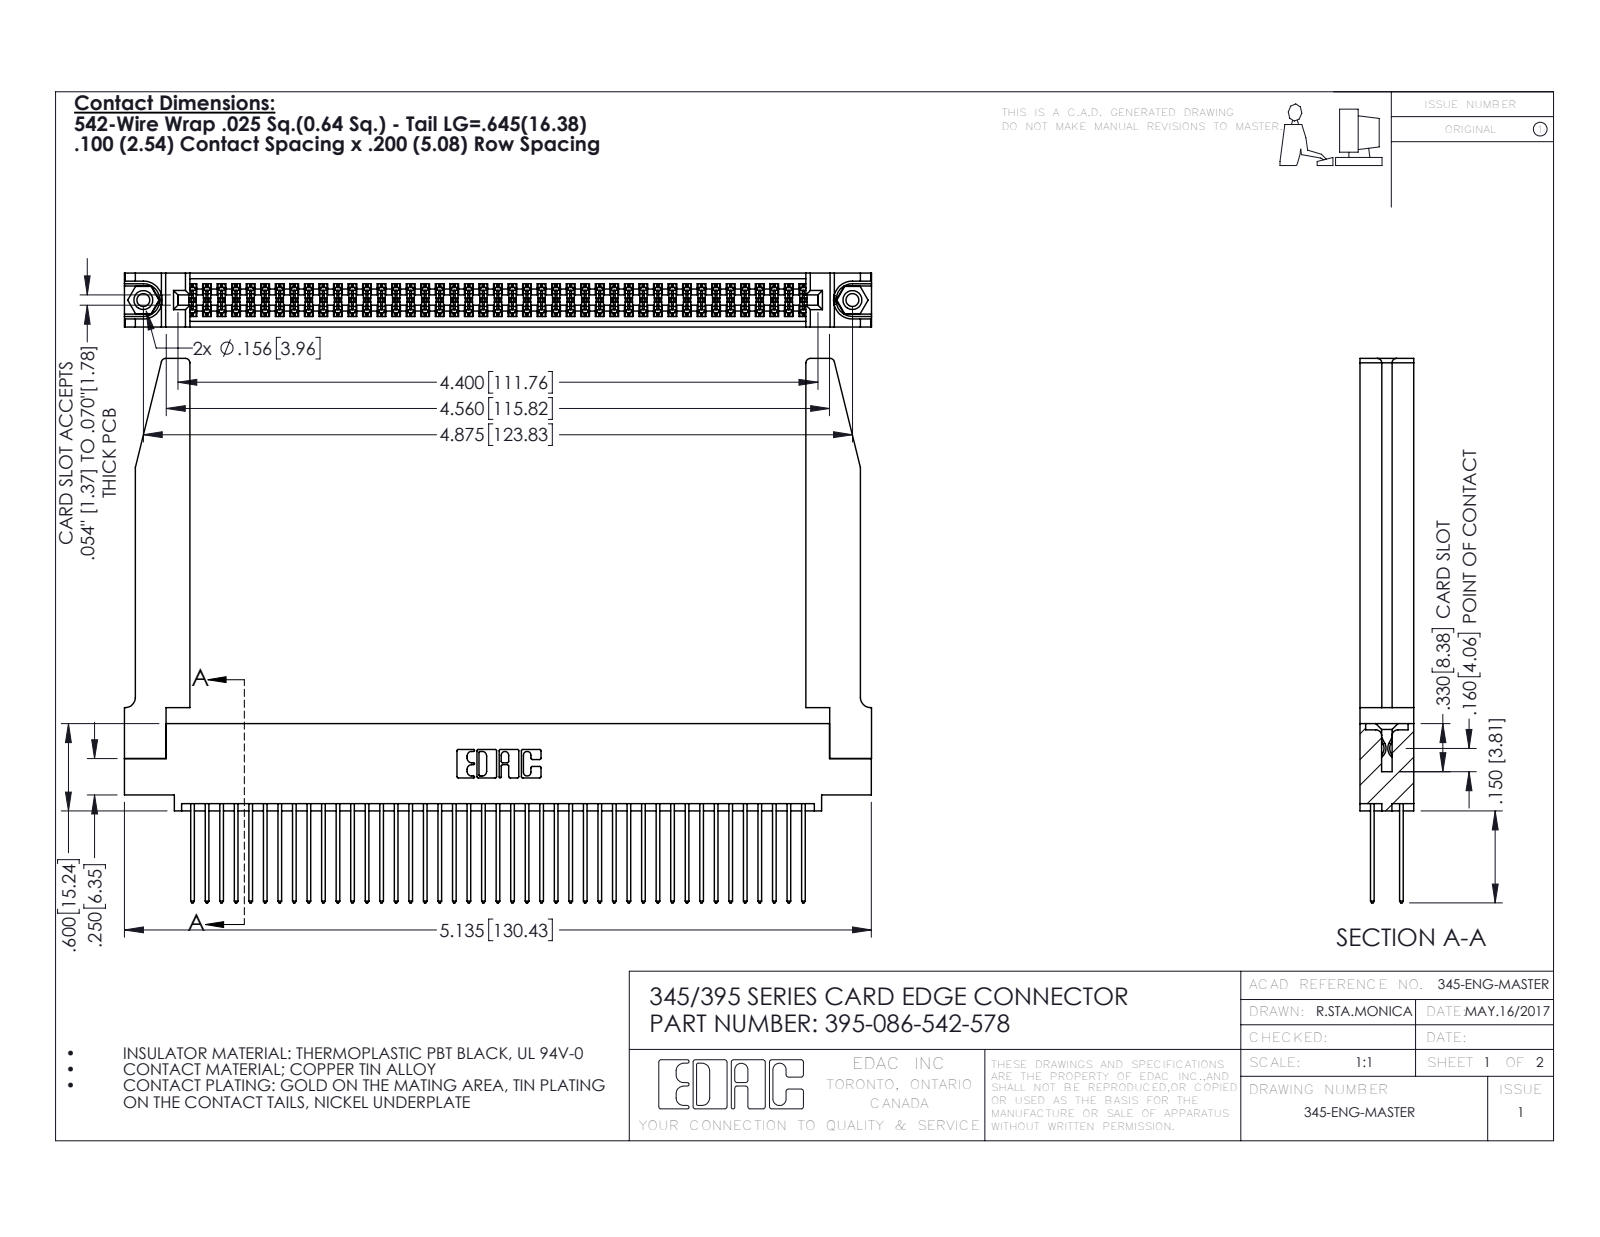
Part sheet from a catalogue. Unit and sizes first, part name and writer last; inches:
Units: inches
Overall size (bounding box): 5.136 × 3.742 × 0.37
Round holes (diameter × count): ⌀0.089 ×2, ⌀0.125 ×2, ⌀0.156 ×2, ⌀0.064 ×1
Round bosses / shafts (diameter × count): ⌀0.155 ×2
Partial cylindrical surfaces — rounded edges, fillets, slot ends (radius × count): R0.006 ×129, R0.01 ×86, R0.01 ×22, R0.03 ×8, R0.007 ×6, R0.031 ×6, R0.026 ×3, R0.014 ×2
Main face-to-face distances: 0.072, 0.298, 0.37, 0.2, 0.098, 0.272, 0.025, 0.225, 0.175, 0.148
Hole centre spacings: 0.27, 4.639, 4.875
Volume: 1.268 in³ · Surface area: 43.48 in²
Bodies: 91 solids, 4664 faces (3064 planar, 1548 cylindrical, 52 other)
Part name (STEP PRODUCT): 345-250-001_345-250-001-102; 345-292-001_345-293-142; 345-220-078_345-220-078; 395-086-542-578 (+1 more)
STEP written by: SolidWorks 2016 (CONFIG_CONTROL_DESIGN)
